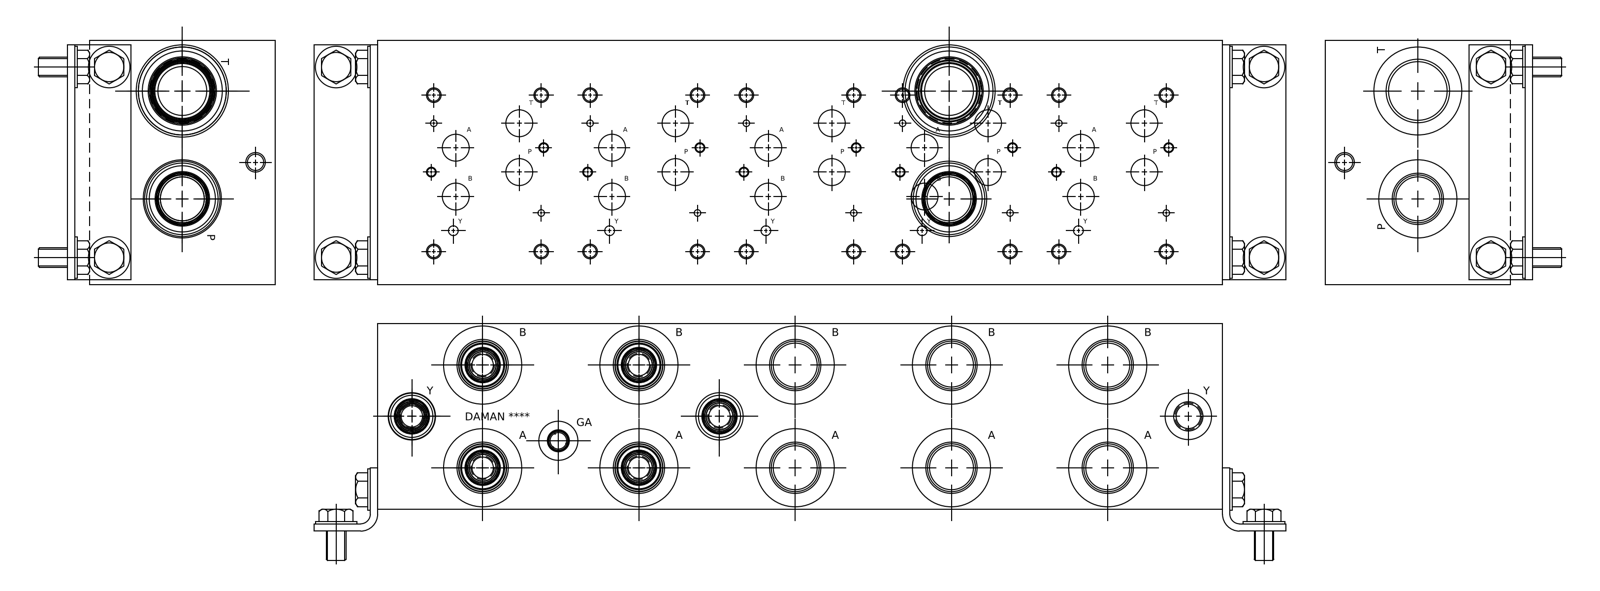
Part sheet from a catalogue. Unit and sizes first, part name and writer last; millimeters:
Units: millimetres
Overall size (bounding box): 549.25 × 158.75 × 120.65
Round holes (diameter × count): ⌀19.05 ×22, ⌀7.92 ×20, ⌀9.53 ×20, ⌀27 ×11, ⌀31.27 ×11, ⌀33.76 ×11, ⌀49.12 ×11, ⌀4.34 ×10, ⌀5.11 ×10, ⌀6.35 ×10, ⌀33.35 ×10, ⌀35.51 ×10
Main face-to-face distances: 120.65, 158.75, 0.79, 549.25, 157.96, 548.46, 547.67, 19.05, 19.84, 138.91
Hole centre spacings: 101.6, 203.2, 304.8, 123.29, 121.53, 143.68, 69.85, 103.23
Volume: 9 938 000 mm³ · Surface area: 438 937 mm²
Bodies: 1 solid, 1049 faces (511 planar, 202 cylindrical, 336 other)
Part name (STEP PRODUCT): Part_AD07HP054S_3D
STEP written by: Autodesk Inventor 2021 (AUTOMOTIVE_DESIGN)
